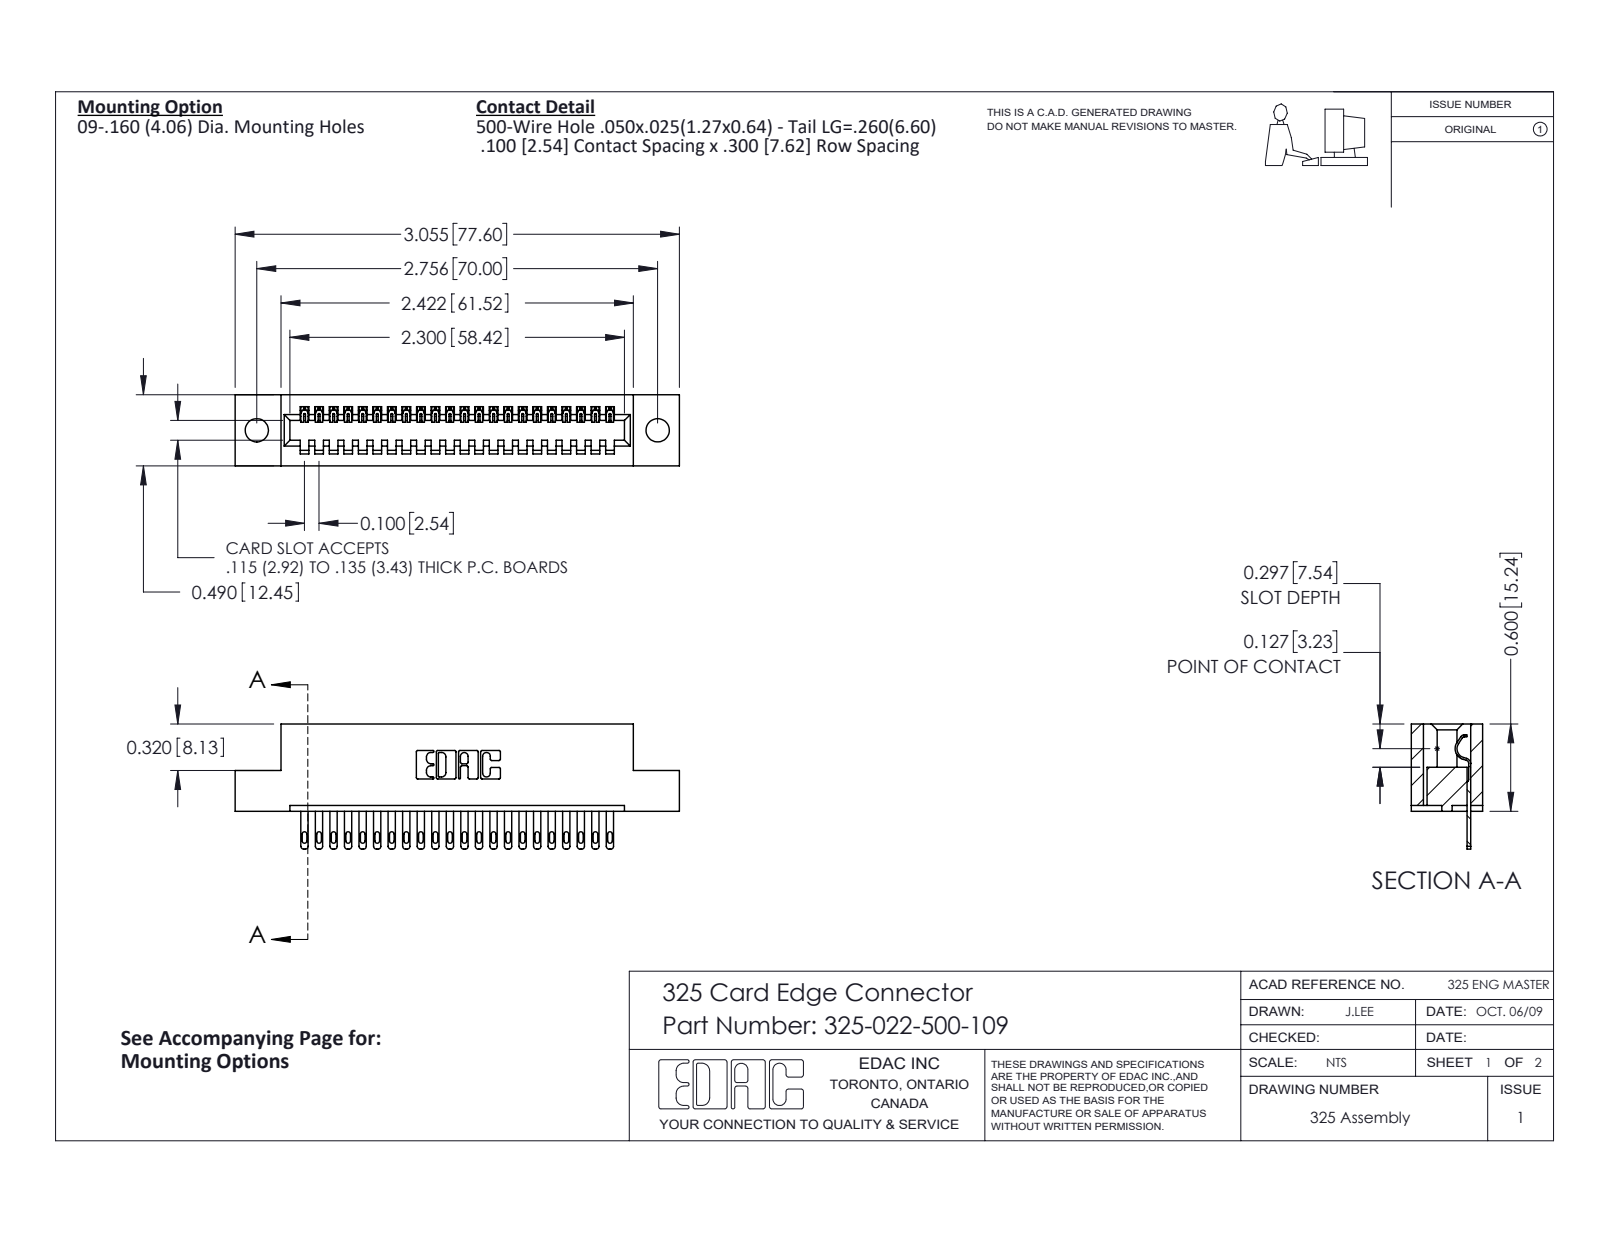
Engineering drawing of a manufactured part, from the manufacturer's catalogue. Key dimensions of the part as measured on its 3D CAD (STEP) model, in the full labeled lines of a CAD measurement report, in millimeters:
Part name (STEP PRODUCT): 325-292-001_325-293-100; 325 Part_.160 TH; 325-022-500-109
STEP written by: SolidWorks 2016 (CONFIG_CONTROL_DESIGN)
Units: millimetres
Bodies: 23 solids, 1302 faces (862 planar, 440 cylindrical, 0 other)
Overall size (bounding box): 77.6 × 21.8 × 12.4
Volume: 9 470 mm³ · Surface area: 9 961 mm²
Round holes (diameter × count): ⌀4.1 ×2
Partial cylindrical surfaces — rounded edges, fillets, slot ends (radius × count): R0.2 ×44, R0.4 ×44, R0.5 ×44, R0.3 ×22, R0.2 ×6, R0.8 ×6, R0.7 ×3, R0.4 ×1
Main face-to-face distances: 2.1, 10.3, 7.6, 12.4, 2.7, 9.7, 0.6, 1, 8.3, 2.5
Hole centre spacings: 70
